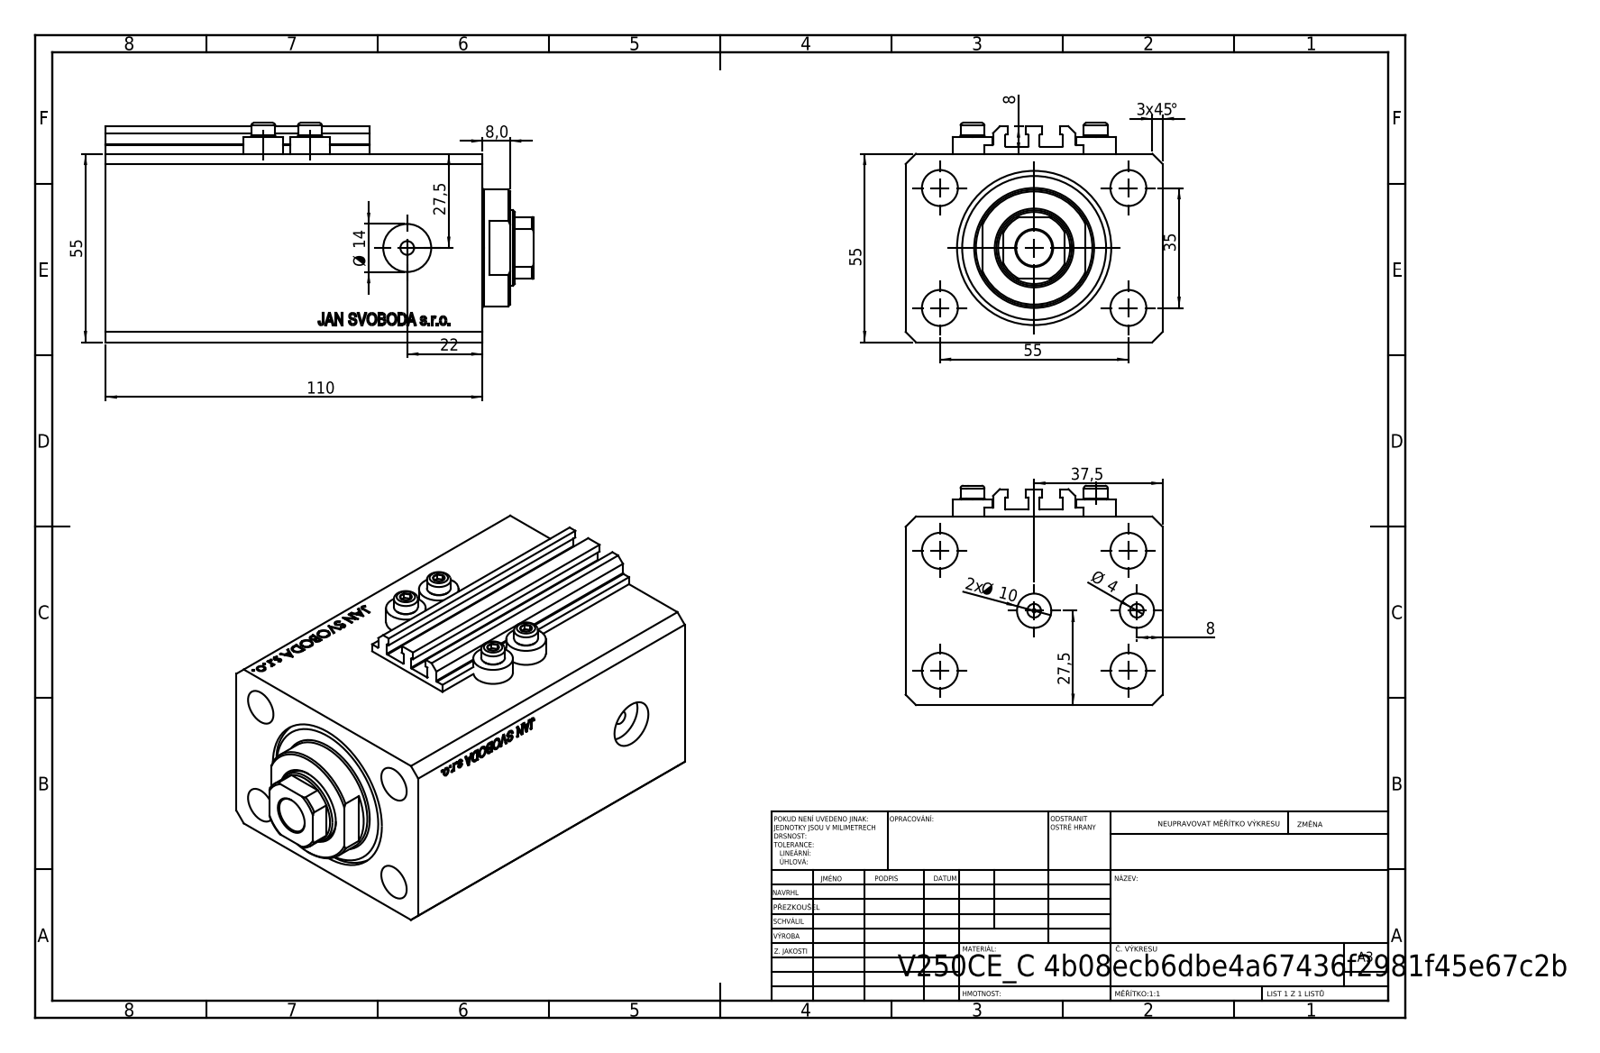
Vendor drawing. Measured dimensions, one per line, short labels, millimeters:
name: V250CE_C_VCP; ALLEN BOLT V250CE; V250CE_VC_C; V250CE_C_Body
written by: SolidWorks 2019 (CONFIG_CONTROL_DESIGN)
unit: mm
bodies: 8 solids, 1038 faces (504 planar, 88 cylindrical, 446 other)
size: 124.9 × 75 × 64
volume: 408 491 mm³; area: 94 180 mm²
holes: 8× ⌀4, 5× ⌀10.5, 2× ⌀10, 2× ⌀14, 1× ⌀1.25, 1× ⌀22, 1× ⌀32, 1× ⌀45
bosses: 4× ⌀11.6, 4× ⌀7, 1× ⌀34
rounds: 10× R0.2, 1× R10.5
face distances: 55, 75, 110, 82.9, 27.1, 9.9, 73, 100.1, 8, 3
hole spacings: 32.6, 13.6, 17.68, 35, 36, 38.48, 55, 60.1
